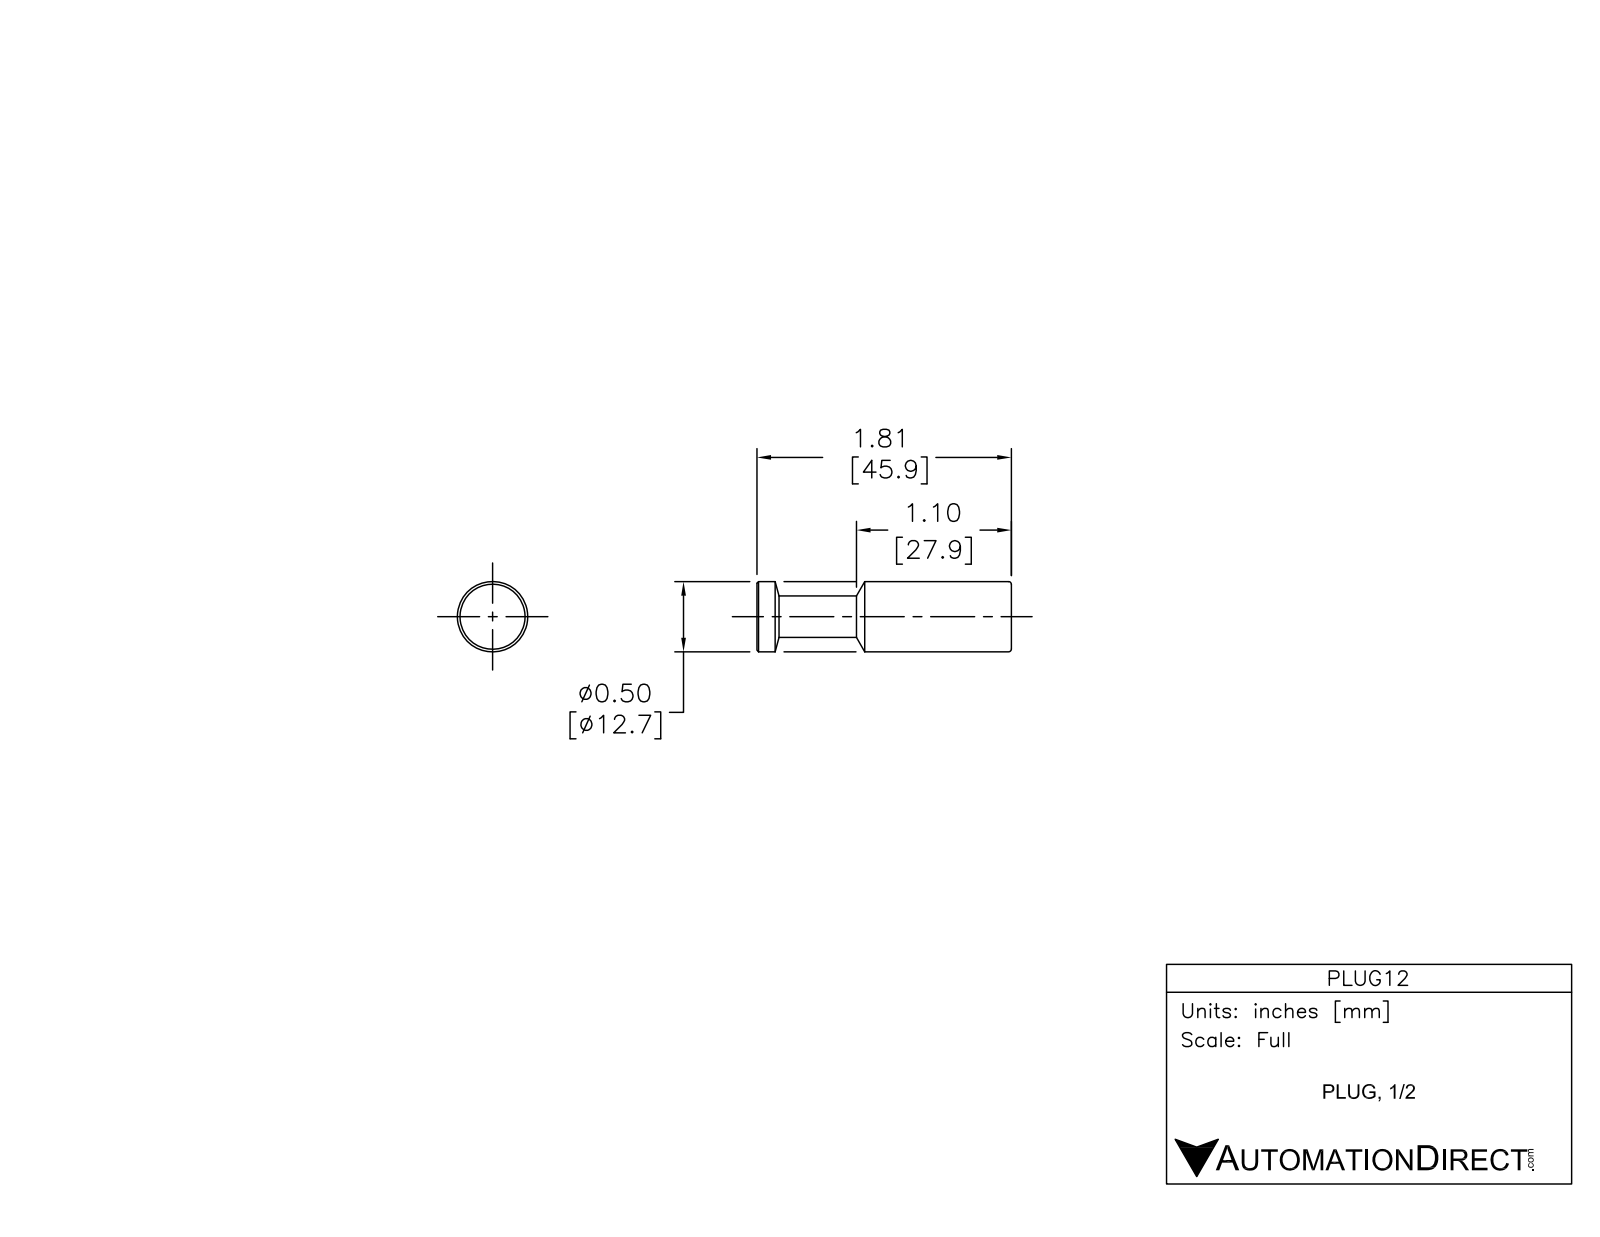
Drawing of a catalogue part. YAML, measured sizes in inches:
part_name: "PLUG12"
step_written_by: "SolidWorks 2015 (AUTOMOTIVE_DESIGN)"
units: inches
bodies: {solids: 1, faces: 16, planar: 2, cylindrical: 6, other: 8}
overall_size: [1.811, 0.5, 0.5]
volume: 0.279
surface_area: 3.003
round_bosses_or_shafts:
  - {diameter: 0.5, count: 1}
  - {diameter: 0.295, count: 1}
face_to_face_distances: [1.811]
